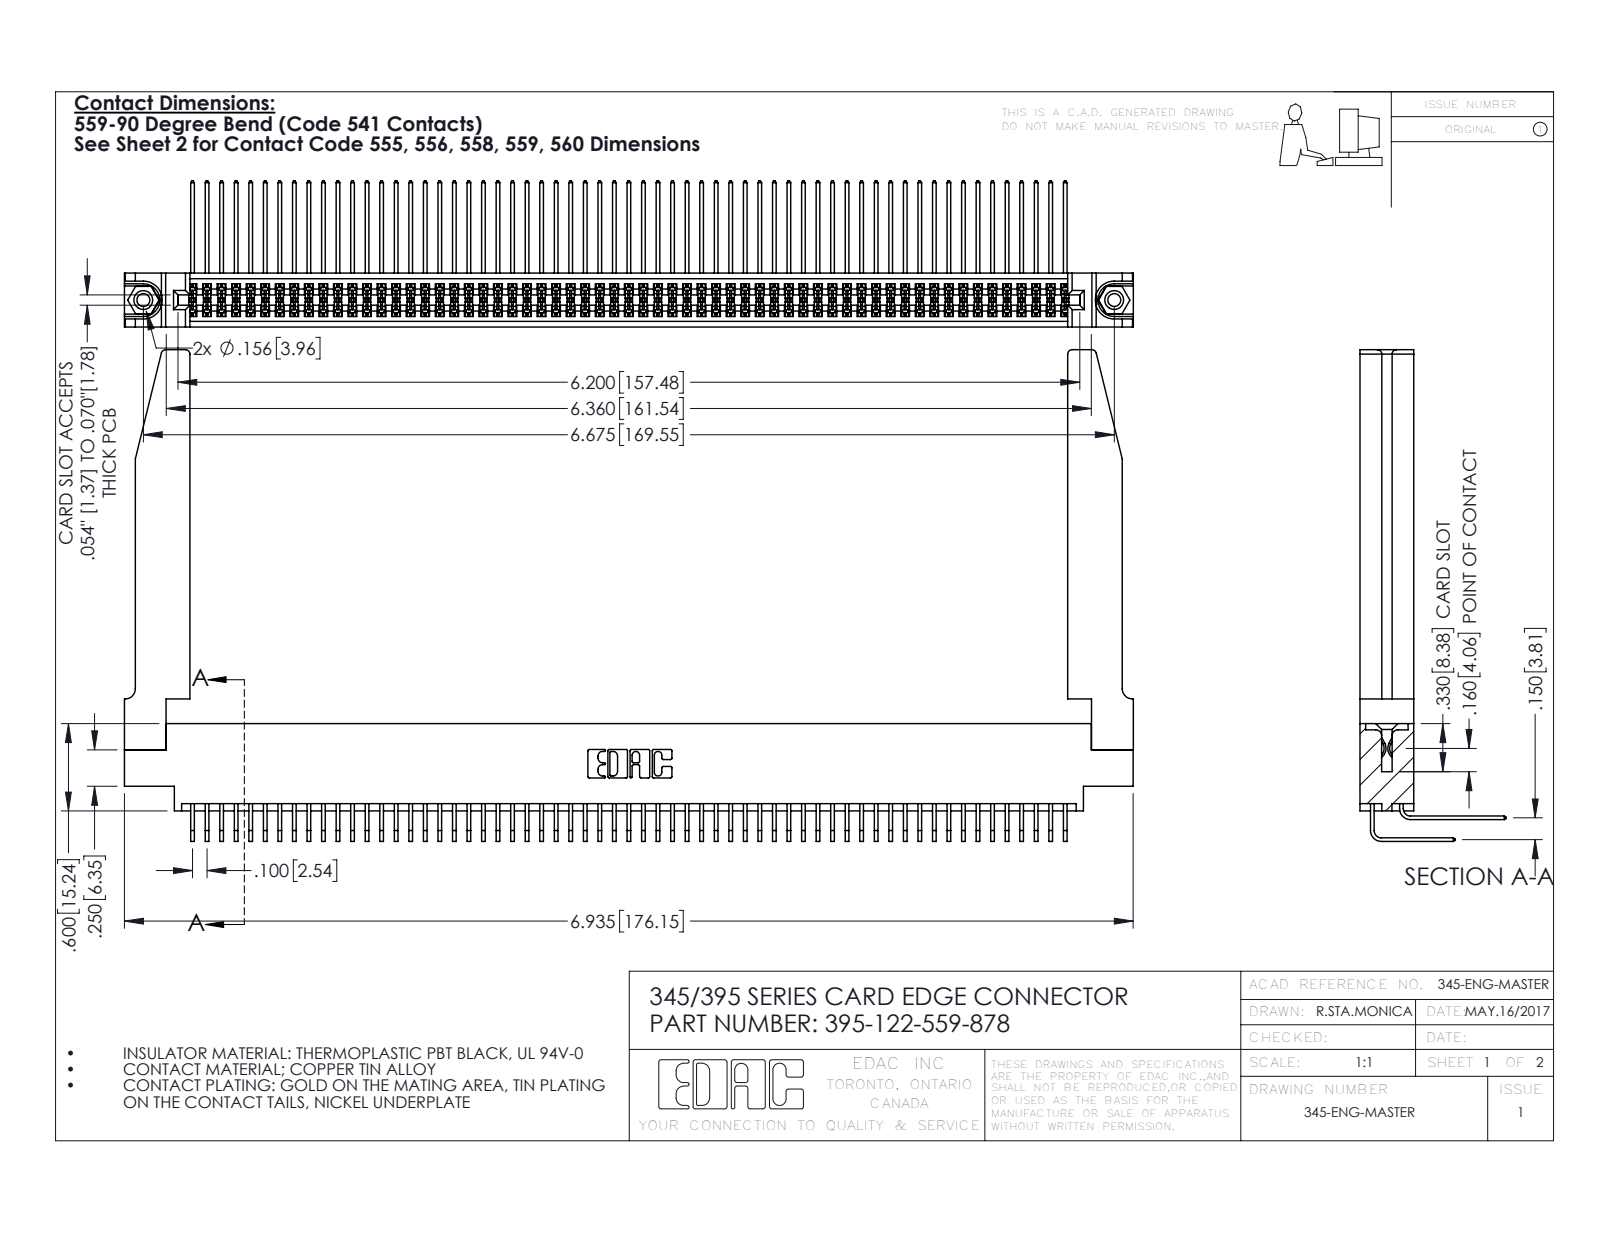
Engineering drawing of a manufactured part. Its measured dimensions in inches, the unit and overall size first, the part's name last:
Units: inches
Overall size (bounding box): 6.936 × 3.379 × 1.005
Round holes (diameter × count): ⌀0.089 ×2, ⌀0.125 ×2, ⌀0.156 ×2, ⌀0.064 ×1
Round bosses / shafts (diameter × count): ⌀0.155 ×2
Partial cylindrical surfaces — rounded edges, fillets, slot ends (radius × count): R0.006 ×183, R0.01 ×22, R0.03 ×8, R0.007 ×6, R0.031 ×6, R0.026 ×3, R0.014 ×2, R0.019 ×2
Main face-to-face distances: 0.072, 0.298, 0.37, 0.098, 0.272, 0.025, 0.2, 0.225, 0.15, 0.175
Hole centre spacings: 0.27, 6.439, 6.675
Volume: 1.565 in³ · Surface area: 57.49 in²
Bodies: 127 solids, 6708 faces (4496 planar, 2160 cylindrical, 52 other)
Part name (STEP PRODUCT): 345-292-001_558 559 Tail - 1; 345-292-001_559 Tail - 2; 345-220-078_345-220-078; 345-250-001_345-250-001-102 (+2 more)
STEP written by: SolidWorks 2016 (CONFIG_CONTROL_DESIGN)
